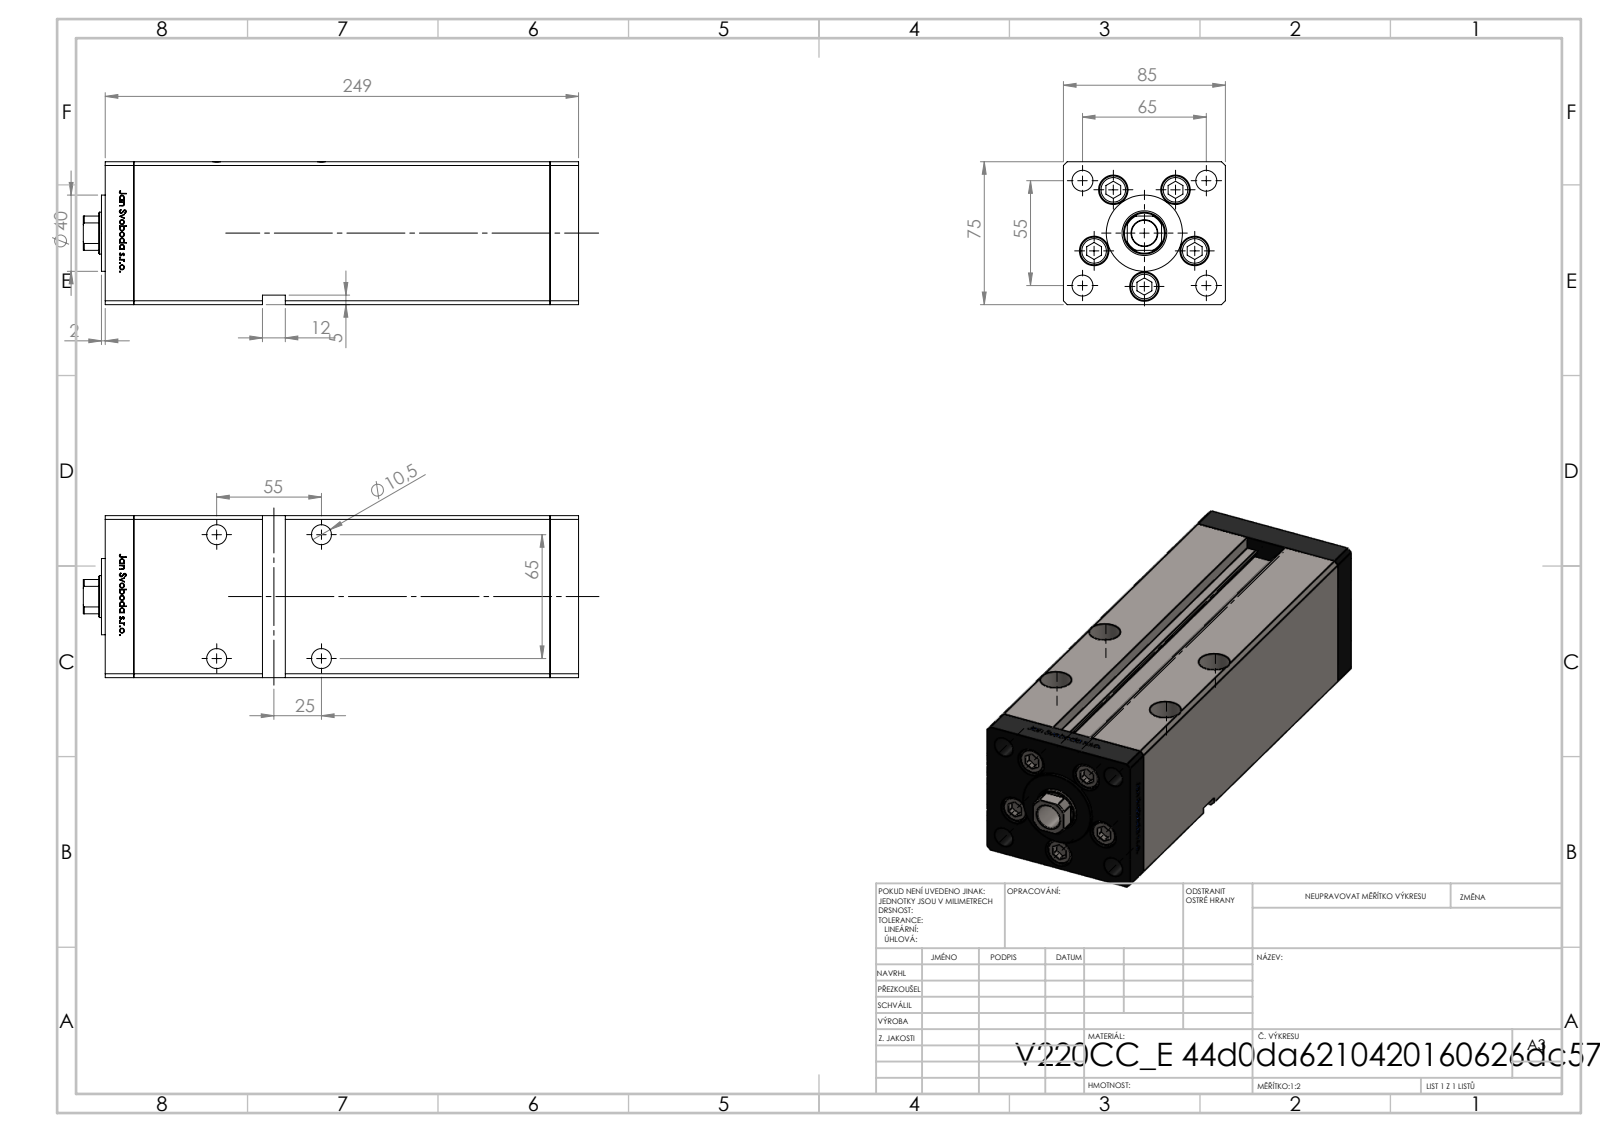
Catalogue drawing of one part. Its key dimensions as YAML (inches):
part_name: "V220C_FRONT_E; ALLEN BOLT; V220C BACK_E; V220C_E MIDDLE (+1 more)"
step_written_by: "SolidWorks 2019 (CONFIG_CONTROL_DESIGN)"
units: inches
bodies: {solids: 14, faces: 1212, planar: 473, cylindrical: 165, other: 574}
overall_size: [10.236, 3.346, 2.953]
volume: 81.83
surface_area: 324.8
round_holes:
  - {diameter: 0.433, count: 9}
  - {diameter: 0.61, count: 5}
  - {diameter: 0.413, count: 4}
  - {diameter: 0.65, count: 4}
  - {diameter: 0.079, count: 2}
  - {diameter: 0.518, count: 2}
  - {diameter: 0.531, count: 1}
  - {diameter: 0.866, count: 1}
  - {diameter: 0.925, count: 1}
round_bosses_or_shafts:
  - {diameter: 0.571, count: 5}
  - {diameter: 0.315, count: 5}
  - {diameter: 1.575, count: 1}
partial_cylinders:
  - {radius: 0.037, count: 2}
  - {radius: 0.413, count: 1}
face_to_face_distances: [3.346, 2.953, 0.591, 8.602, 9.193, 9.783, 0.413, 2.539, 1.348, 2.697]
hole_center_spacings: [1.102, 1.676, 2.165, 2.559, 3.352, 0.664, 0.755, 1.273]
